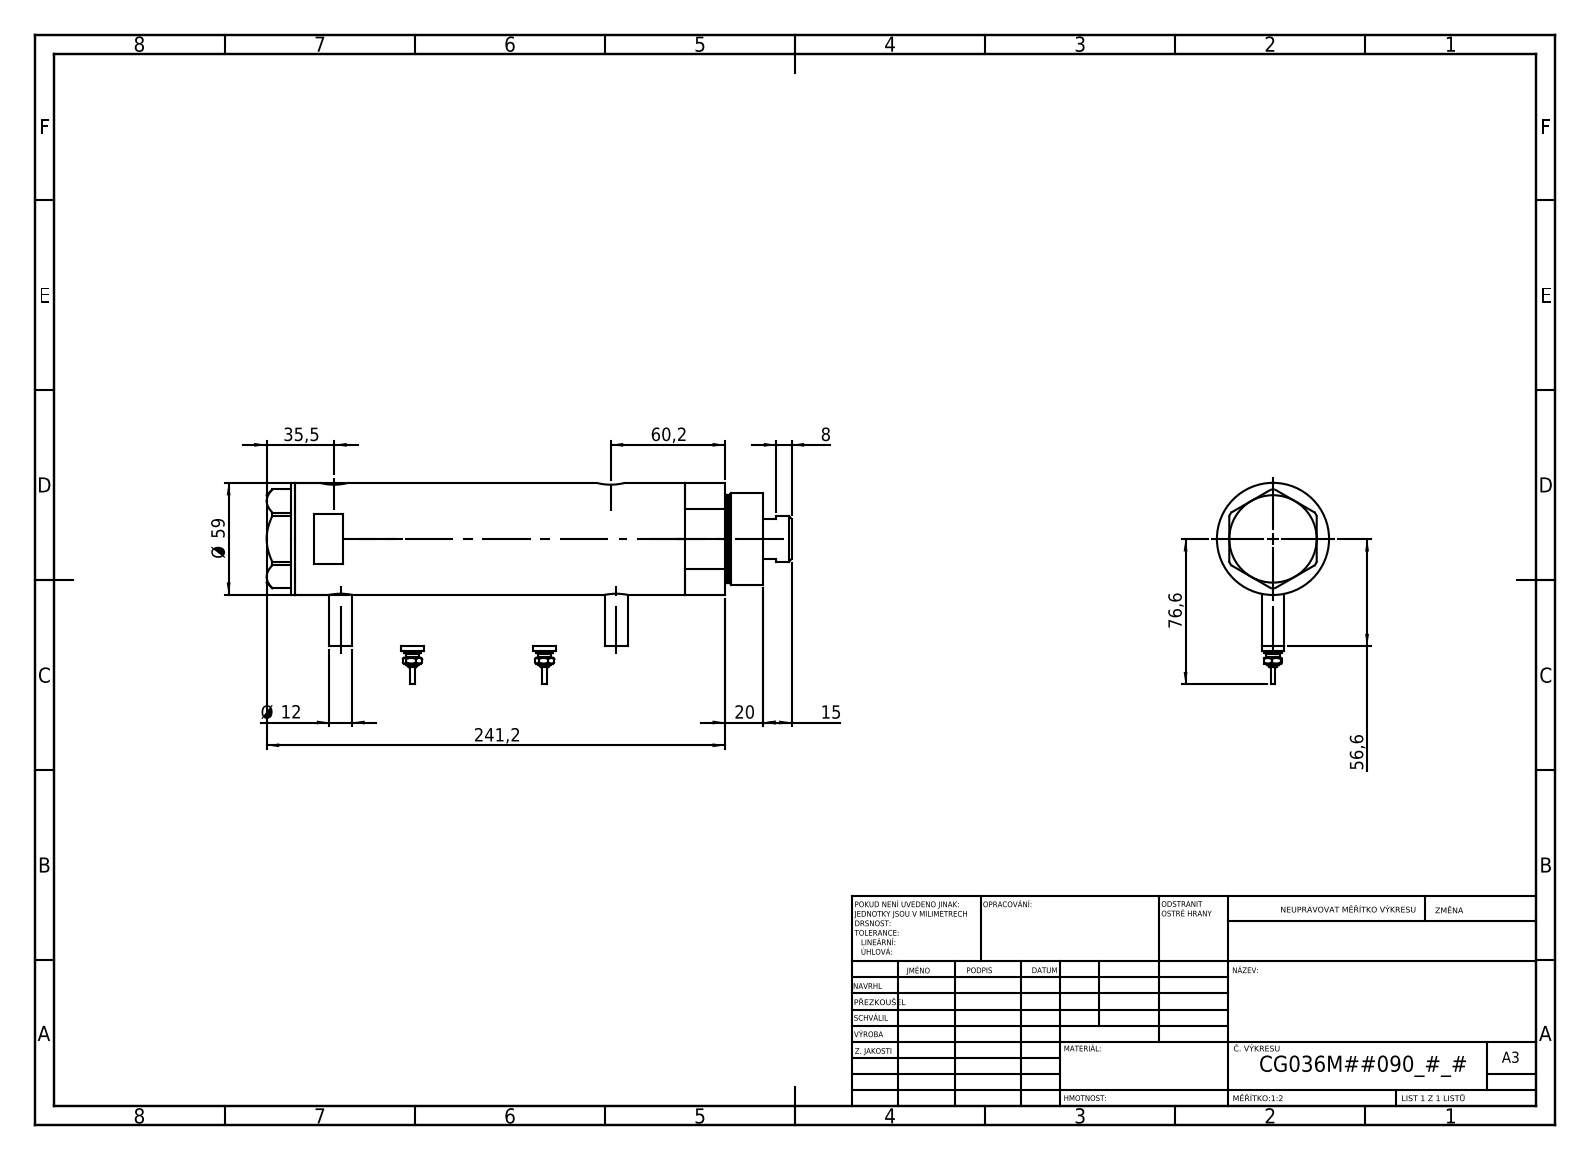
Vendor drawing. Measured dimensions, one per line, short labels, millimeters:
name: V270CG_FRONT; Switch; V270CG_BACK; V270CG_VC (+1 more)
written by: SolidWorks 2019 (CONFIG_CONTROL_DESIGN)
unit: mm
bodies: 6 solids, 212 faces (79 planar, 69 cylindrical, 64 other)
size: 276.2 × 106.1 × 59
volume: 641 086 mm³; area: 128 122 mm²
holes: 2× ⌀9.73, 2× ⌀12.5, 2× ⌀15, 1× ⌀8.5, 1× ⌀25, 1× ⌀26.5, 1× ⌀36, 1× ⌀40, 1× ⌀52
bosses: 4× ⌀12, 2× ⌀9, 2× ⌀7, 2× ⌀4.5, 2× ⌀2.5, 1× ⌀59, 1× ⌀48, 1× ⌀46
face distances: 167.2, 23.5, 143.7, 15, 38.5, 182.2, 2, 261.2, 246.2, 222.7
hole spacings: 2.9, 3.5, 142, 144.9, 145.5, 148.4
